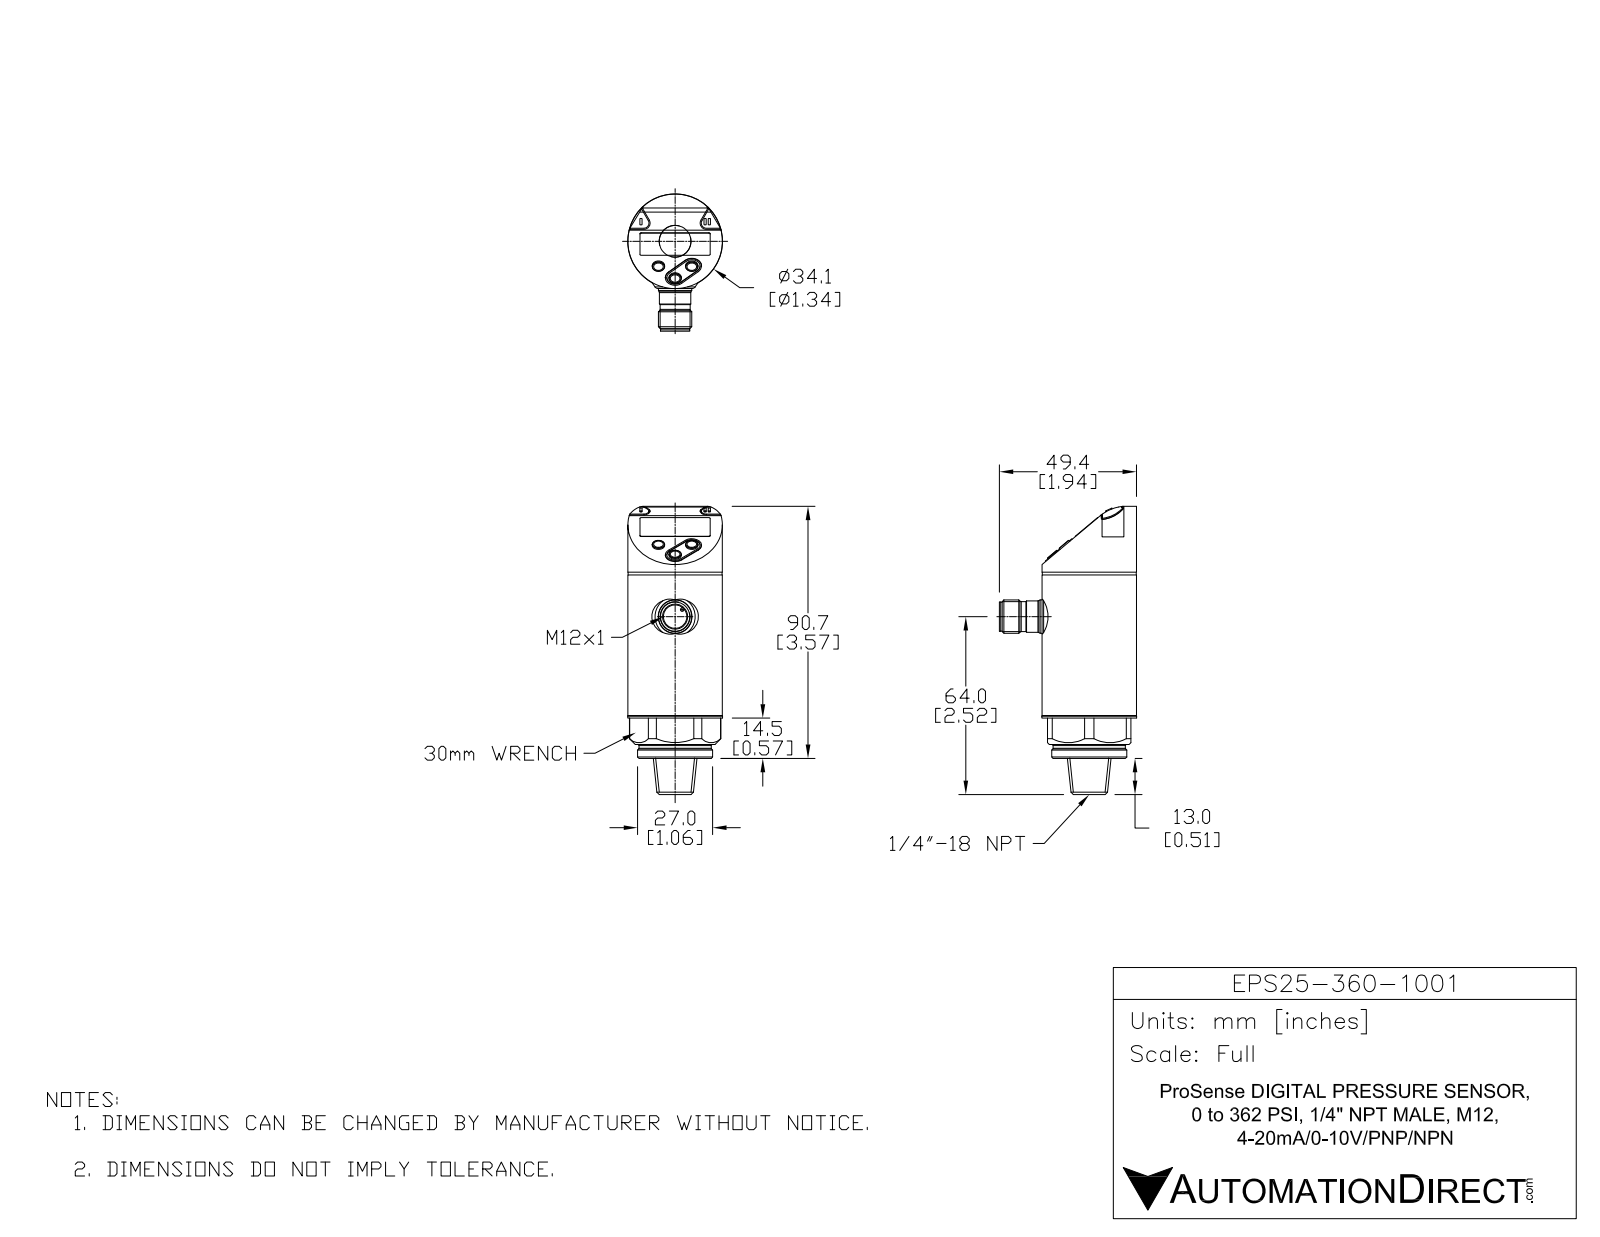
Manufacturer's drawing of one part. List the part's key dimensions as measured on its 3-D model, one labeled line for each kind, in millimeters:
Part name (STEP PRODUCT): EPS25-360-1001
STEP written by: SolidWorks 2016 (AUTOMOTIVE_DESIGN)
Units: millimetres
Bodies: 11 solids, 370 faces (207 planar, 84 cylindrical, 79 other)
Overall size (bounding box): 103.7 × 49.4 × 34.1
Volume: 72 203 mm³ · Surface area: 21 365 mm²
Round holes (diameter × count): ⌀4.2 ×1, ⌀8.45 ×1
Round bosses / shafts (diameter × count): ⌀1.4 ×4, ⌀1 ×4, ⌀34.1 ×1, ⌀34 ×1, ⌀33.8 ×1, ⌀27 ×1, ⌀26 ×1, ⌀12 ×1
Partial cylindrical surfaces — rounded edges, fillets, slot ends (radius × count): R1.8 ×2, R2.2 ×2, R3 ×2, R3.5 ×2, R15 ×2, R0.61 ×1, R6.8 ×1, R16.44 ×1
Main face-to-face distances: 0.68, 11.5, 12.18, 10.68, 1.5, 10, 2, 2.5, 14, 4
